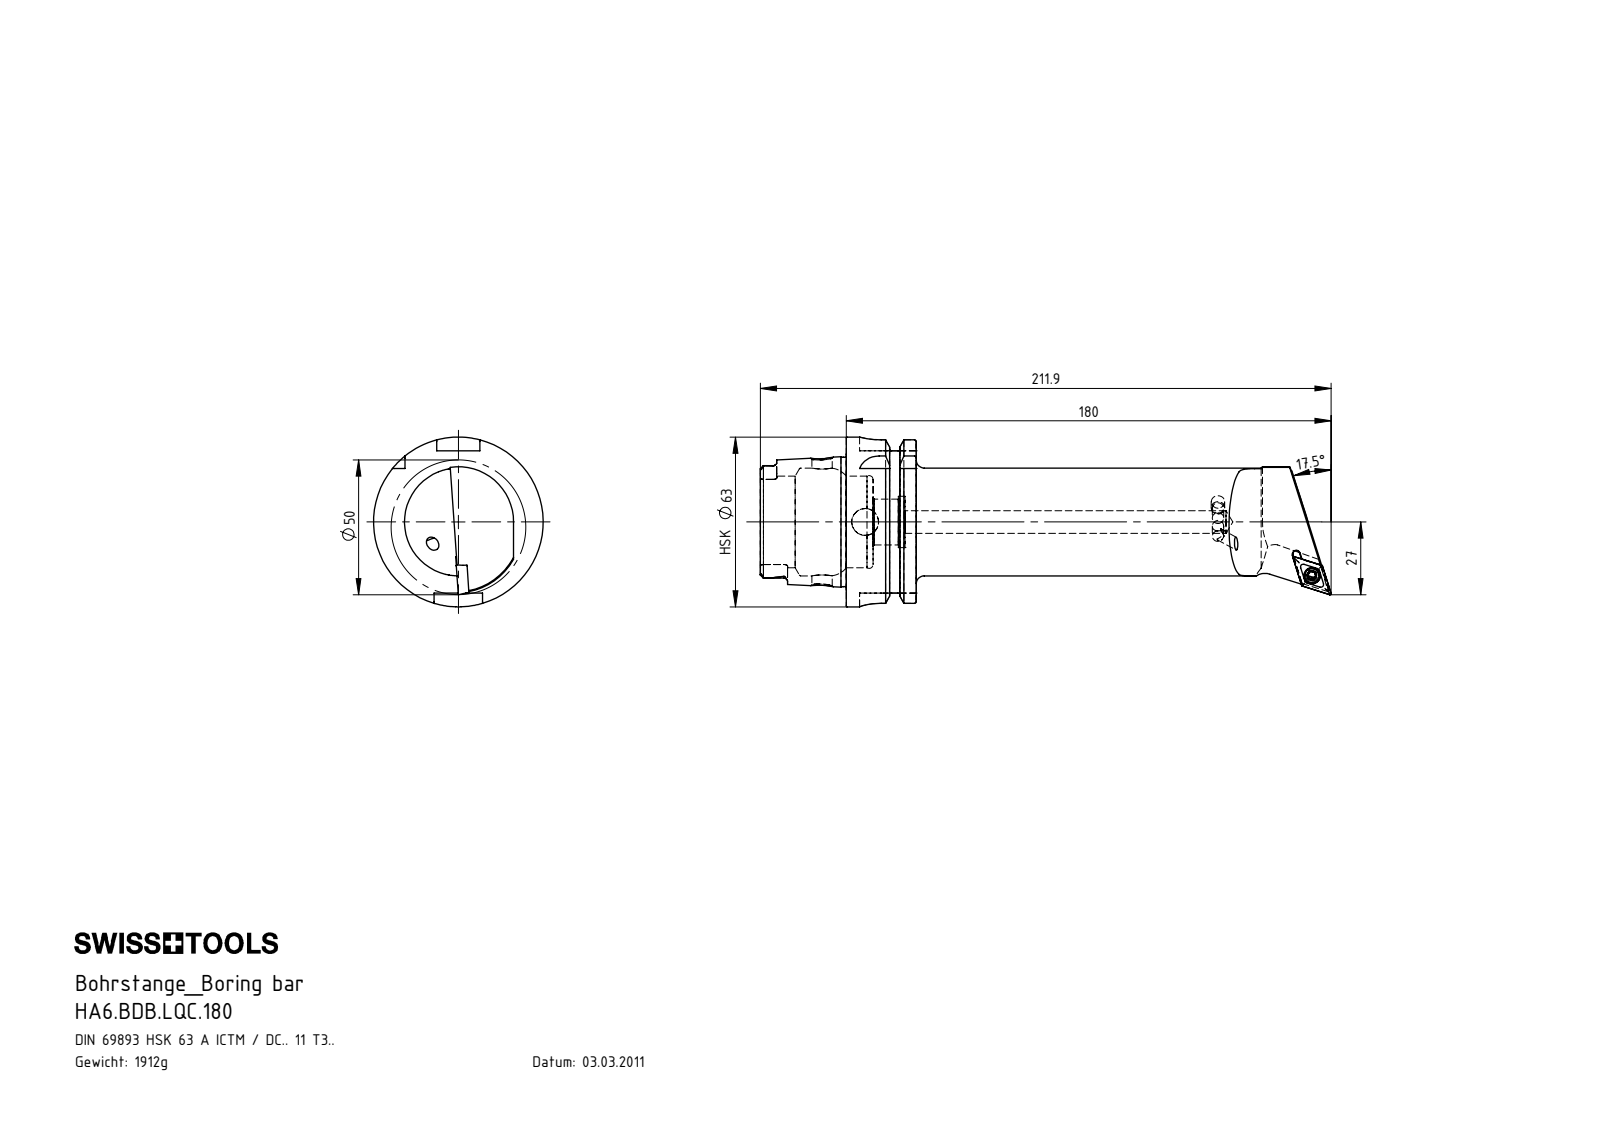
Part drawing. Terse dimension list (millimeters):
name: HA6-BDB.LQC.180; KVT_MB_600_050; WCB-ER2.001.009_A; DCMT11T304 (+1 more)
written by: SolidWorks 2012 (CONFIG_CONTROL_DESIGN)
unit: mm
bodies: 5 solids, 310 faces (76 planar, 91 cylindrical, 143 other)
size: 211.9 × 63 × 63
volume: 243 274 mm³; area: 44 640 mm²
holes: 2× ⌀4.2, 1× ⌀3.3, 1× ⌀4, 1× ⌀4.4, 1× ⌀5, 1× ⌀6.1, 1× ⌀7.5, 1× ⌀8.4, 1× ⌀10, 1× ⌀17, 1× ⌀19, 1× ⌀34
bosses: 1× ⌀63, 1× ⌀54.95, 1× ⌀47.94, 1× ⌀5.25, 1× ⌀5, 1× ⌀4
rounds: 6× R0.34, 6× R0.59, 6× R1.4, 4× R8, 2× R2.82, 2× R2.88, 1× R1.25, 1× R6
face distances: 25.95, 16, 9.95, 31.9, 41.85, 57.85, 52.8, 21.8, 11.85, 53.7
